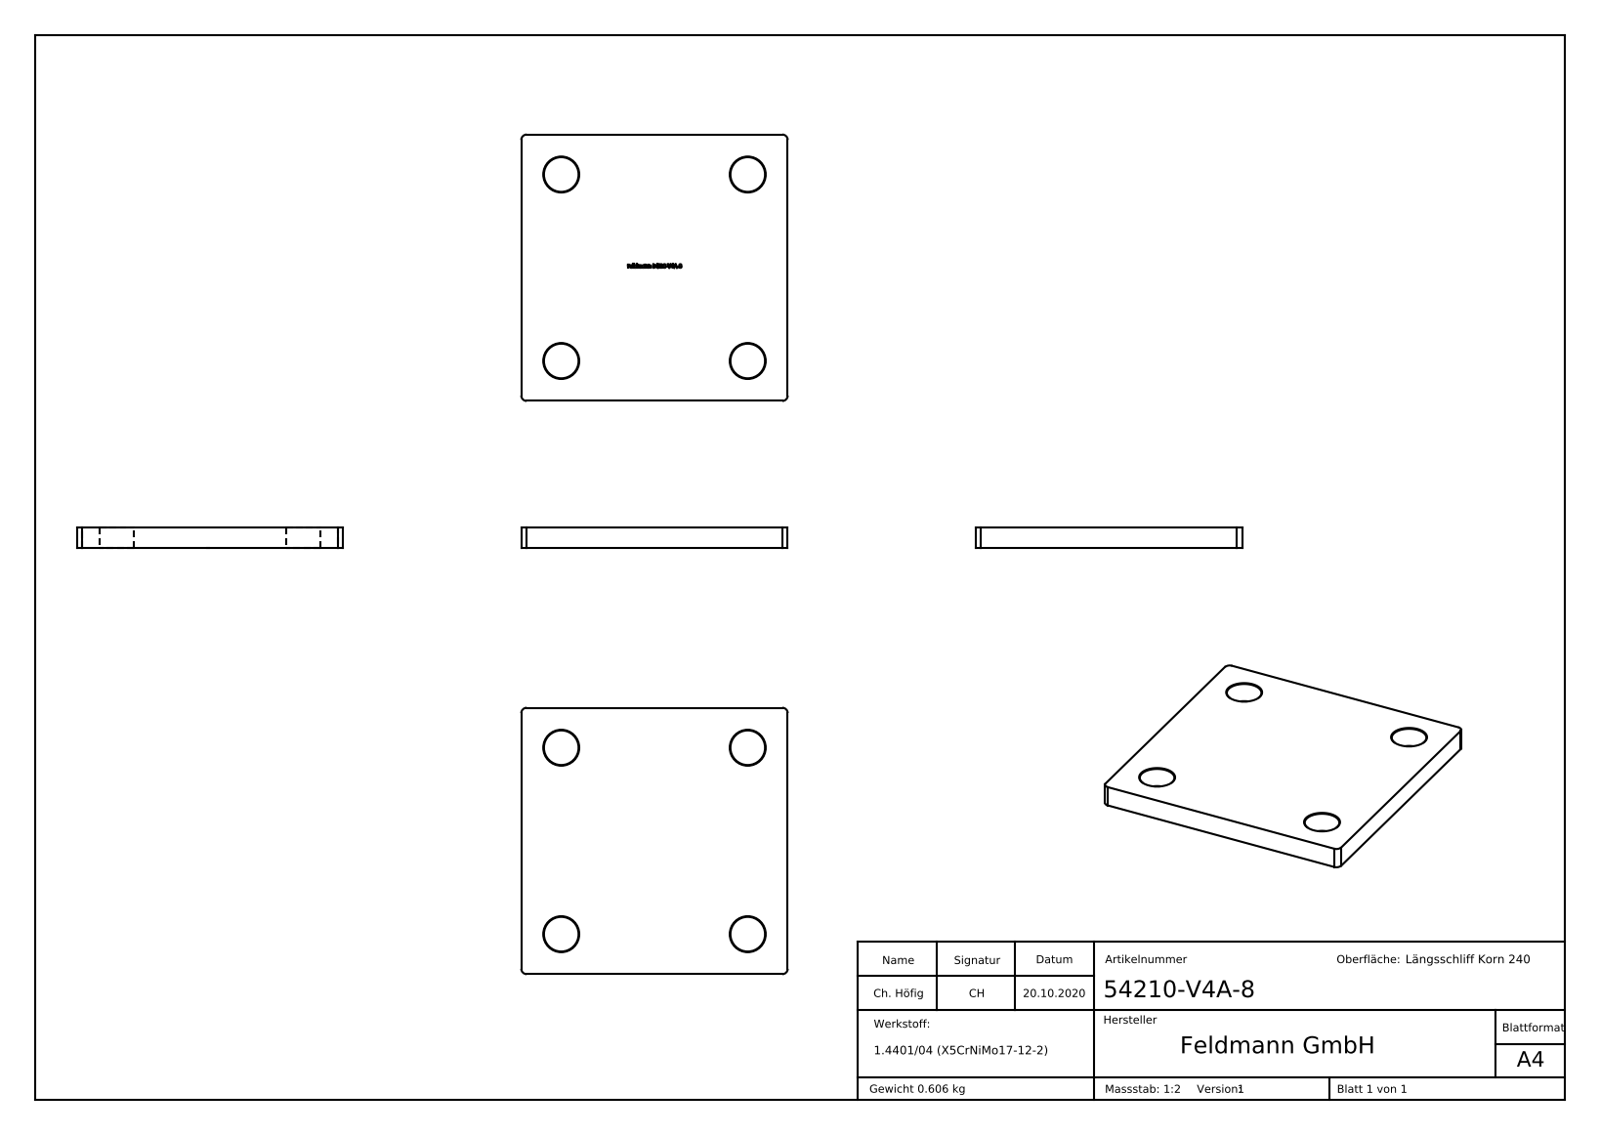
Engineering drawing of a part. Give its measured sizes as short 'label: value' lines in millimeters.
name: 54210-V4A-8
written by: SolidWorks 2018 (CONFIG_CONTROL_DESIGN)
unit: mm
bodies: 1 solid, 274 faces (158 planar, 12 cylindrical, 104 other)
size: 100 × 100 × 8
volume: 75 714 mm³; area: 23 374 mm²
holes: 4× ⌀13
rounds: 4× R2
face distances: 8, 100, 7.9, 50, 0.44, 0.88, 10.74, 2.97, 2.01, 12.75
hole spacings: 70, 98.99
